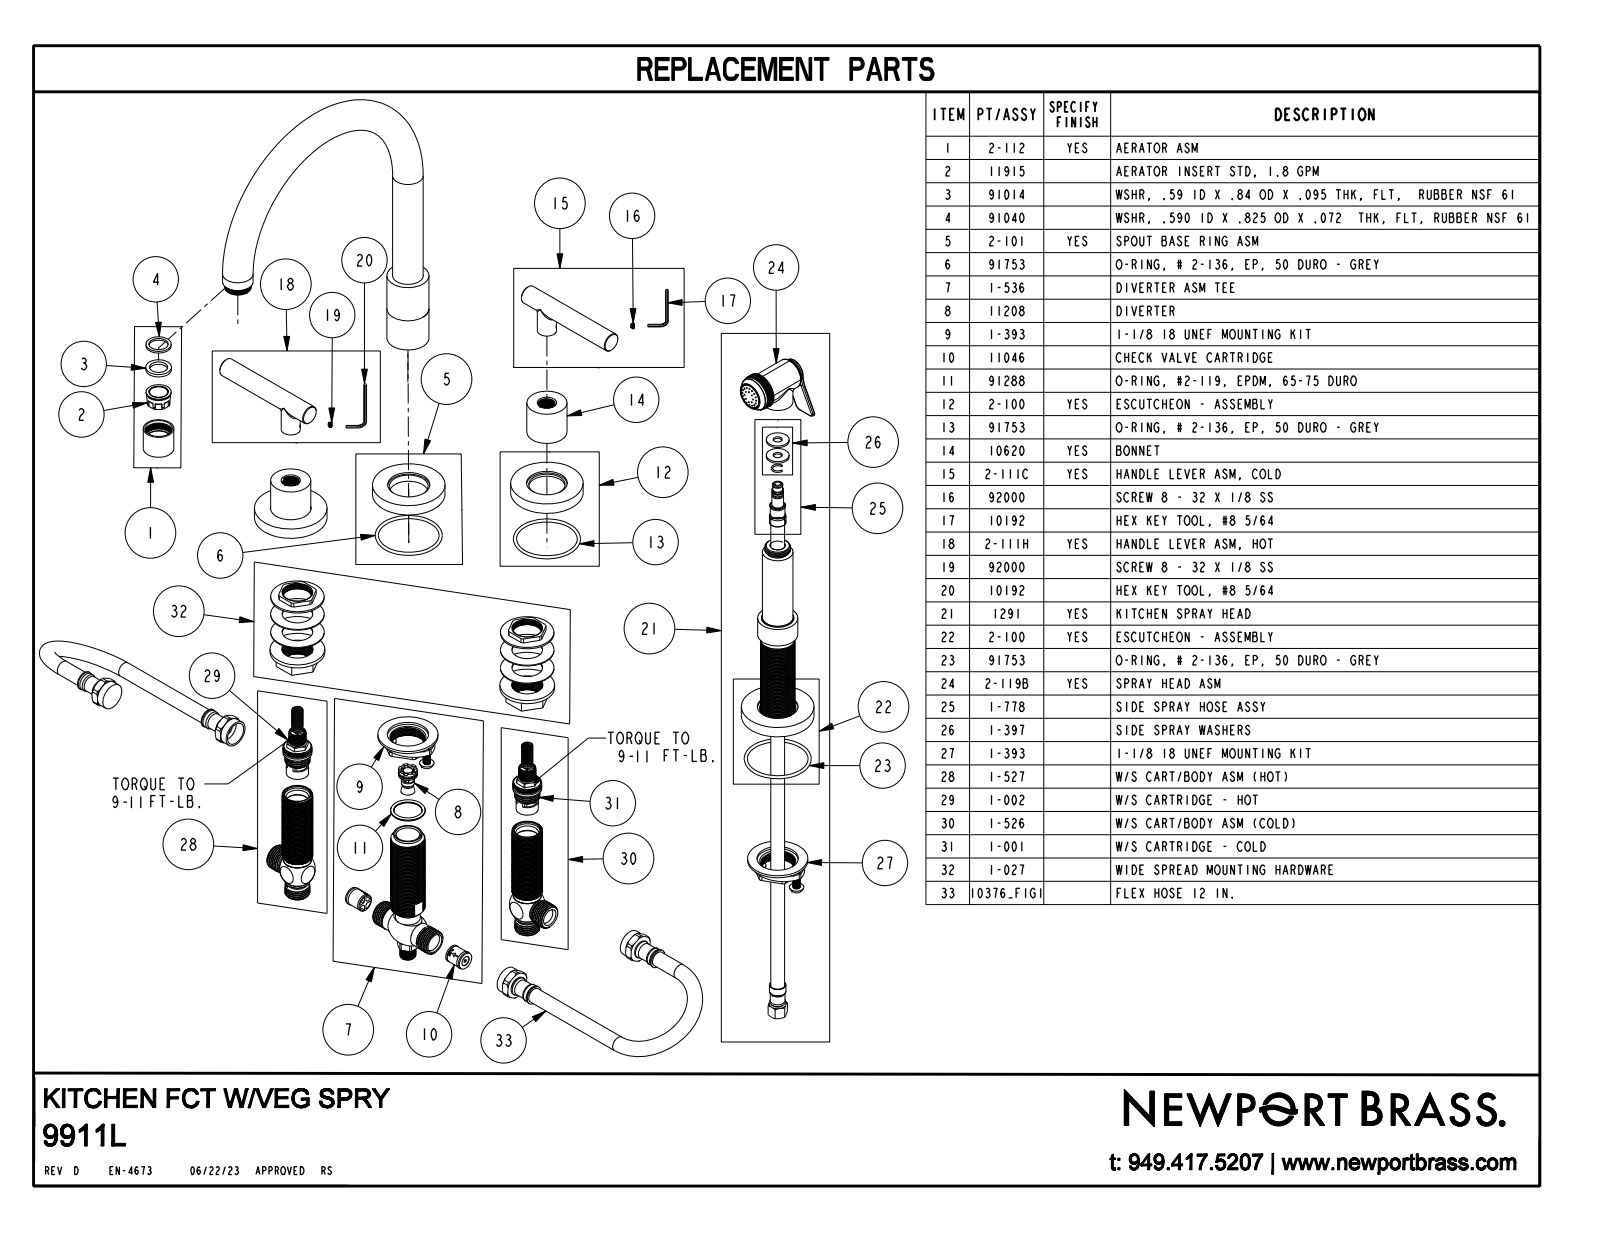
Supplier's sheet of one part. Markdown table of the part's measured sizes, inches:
| quantity | value |
| --- | --- |
| part name | 9911L |
| STEP written by | CREO PARAMETRIC BY PTC INC, 2018400 (AUTOMOTIVE_DESIGN) |
| units | inches |
| bodies | 6 solids, 600 faces (291 planar, 203 cylindrical, 106 other) |
| overall size | 18.176 × 11.248 × 9.765 |
| volume | 34.84 in³ |
| surface area | 171.9 in² |
| round holes (diameter × count) | 0.06 × 1, 0.231 × 1, 0.968 × 1, 1.005 × 1 |
| round bosses / shafts (diameter × count) | 2.375 × 4, 1 × 3, 0.625 × 3, 1.313 × 2, 1.375 × 1, 1.313 × 1, 1.11 × 1, 1.023 × 1 |
| partial cylindrical surfaces (radius × count) | 0.04 × 10, 0.07 × 5, 0.06 × 4, 0.156 × 2, 0.16 × 2, 0.332 × 1, 0.34 × 1, 0.385 × 1 |
| main face-to-face distances | 0.375, 1.483, 1.108, 0.131, 5.698, 5.323, 4.215, 2.81, 2.435, 1.327 |
